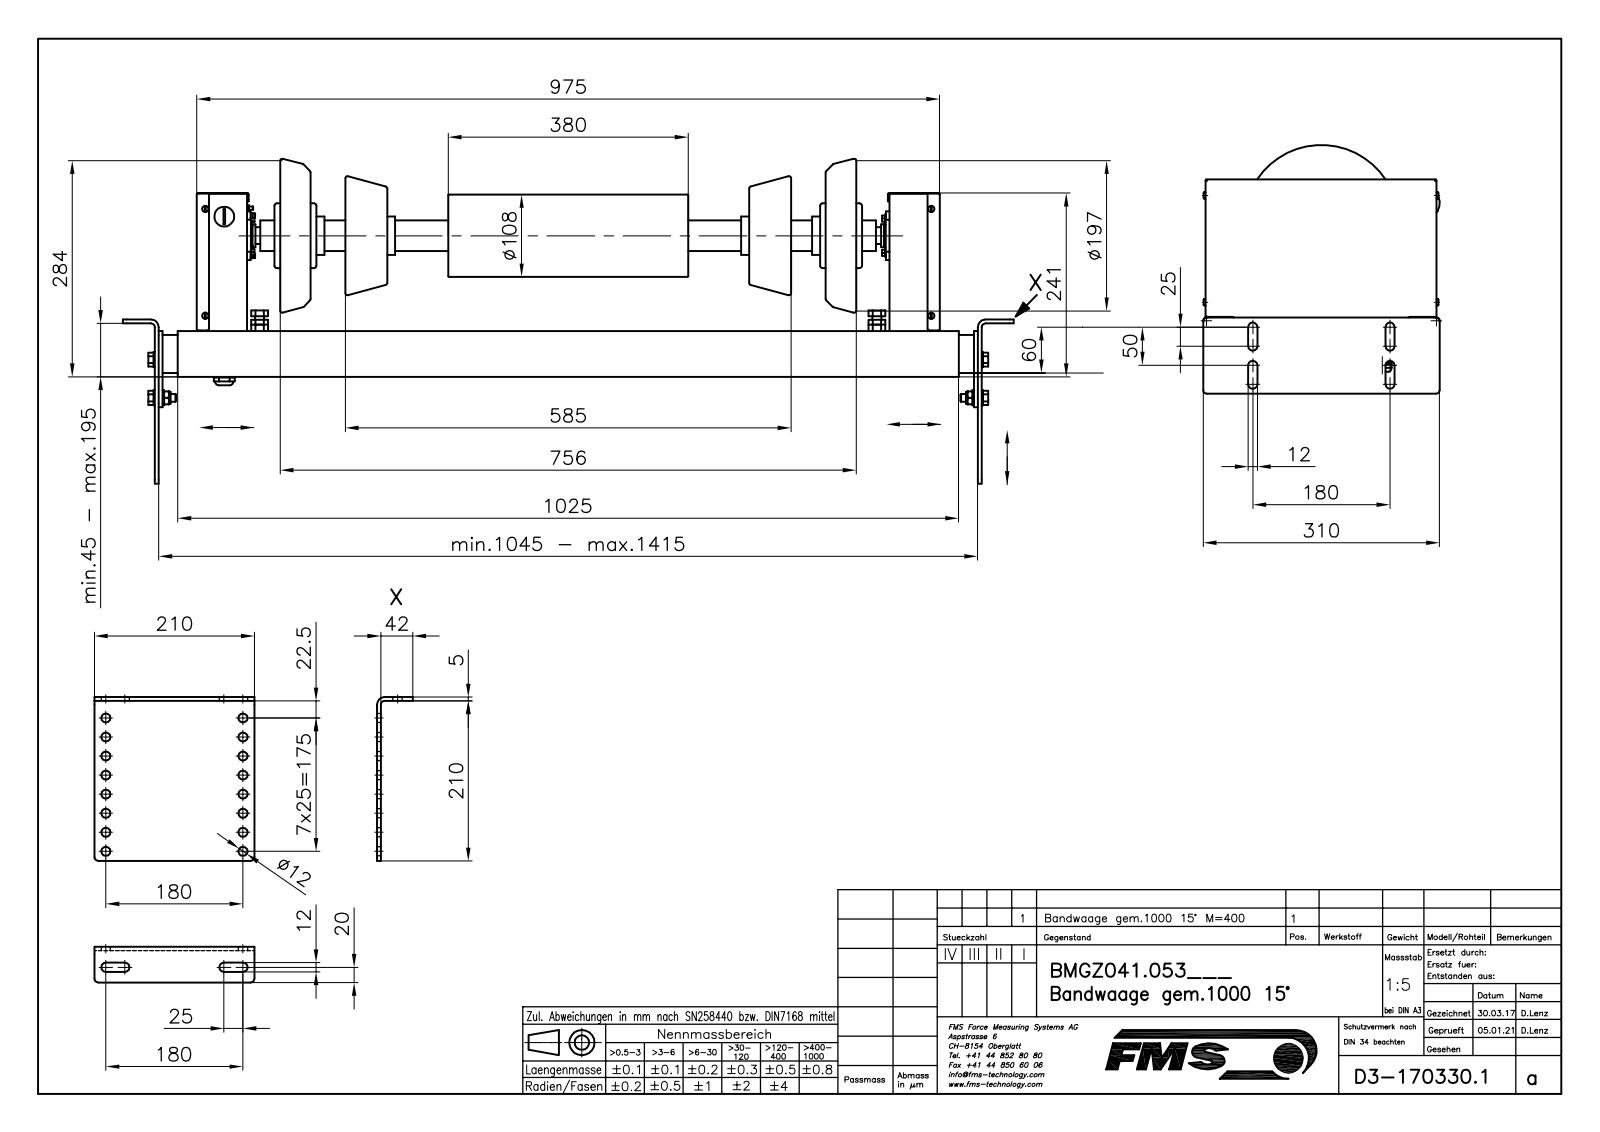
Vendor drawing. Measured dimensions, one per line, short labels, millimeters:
name: B1703301_STP; B50108; 6KT-SCHRAUBE_M12X30; ZYL_SCHR__M4X8 (+8 more)
written by: Mechanical Desktop 2009 (CONFIG_CONTROL_DESIGN)
unit: mm
bodies: 179 solids, 2932 faces (1427 planar, 1058 cylindrical, 447 other)
size: 1169 × 426.14 × 310.2
volume: 8 234 000 mm³; area: 3 479 000 mm²
holes: 17× ⌀12, 6× ⌀5, 4× ⌀3.5, 4× ⌀4.9, 4× ⌀5.3, 4× ⌀5.8, 4× ⌀6.4, 4× ⌀6.91, 4× ⌀8.68, 4× ⌀8.75, 4× ⌀10, 4× ⌀10.5
bosses: 11× ⌀12, 8× ⌀10, 8× ⌀8.2, 8× ⌀4.2, 7× ⌀5, 6× ⌀20, 6× ⌀8, 4× ⌀16
rounds: 34× R2, 24× R1, 16× R4, 16× R5, 12× R6, 8× R3.5, 6× R2.25, 4× R0.5
face distances: 4, 5, 1, 51, 270, 36, 56, 3, 50, 66
hole spacings: 25, 181.73, 50, 186.82, 75, 195, 100, 180
